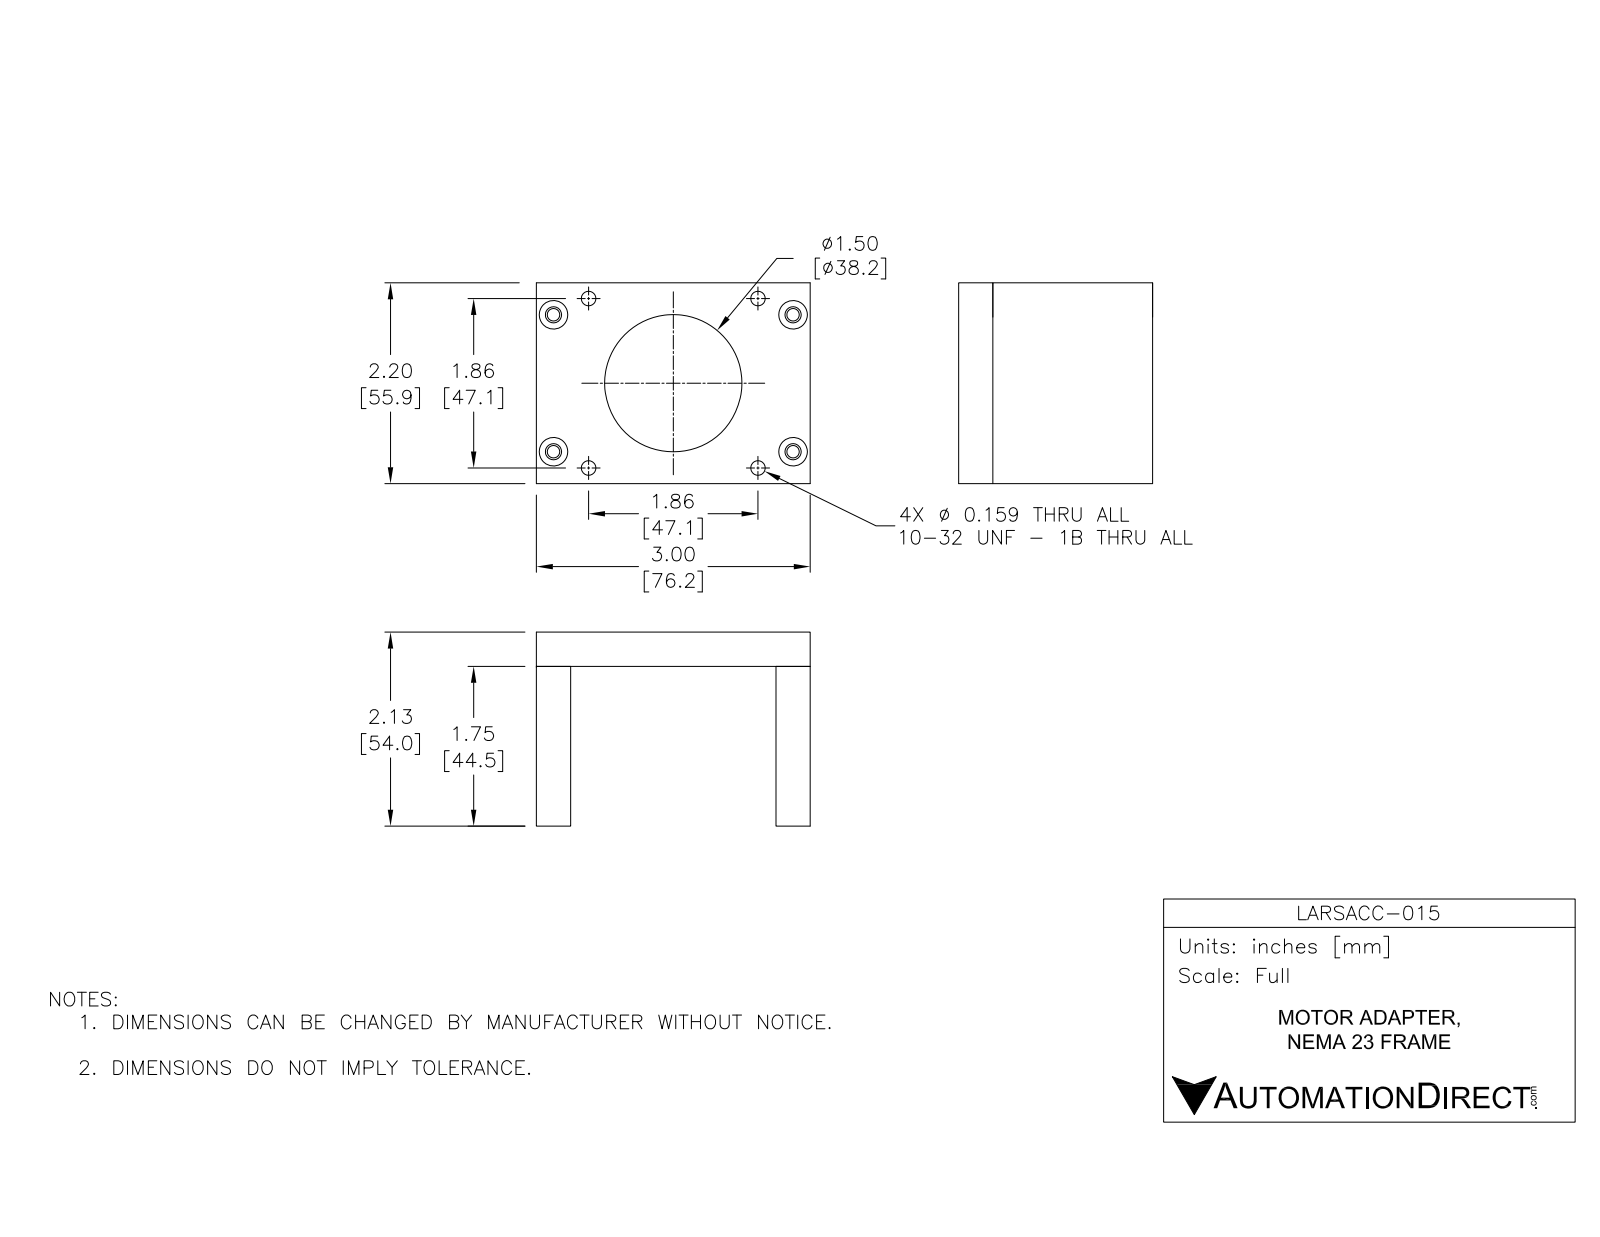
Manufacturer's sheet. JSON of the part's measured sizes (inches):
{"part_name": "LARSACC-015", "step_written_by": "SolidWorks 2015 (AUTOMOTIVE_DESIGN)", "units": "inches", "bodies": {"solids": 3, "faces": 88, "planar": 22, "cylindrical": 46, "other": 20}, "overall_size": [3, 2.2, 2.125], "volume_in3": 4.488, "surface_area_in2": 40.97, "round_holes": [[0.159, 10], [0.136, 4], [0.177, 4], [0.313, 4], [1.504, 1]], "face_to_face_distances": [0.375, 3, 2.625, 0.375, 2.25, 2.625, 2.2, 1.75, 2.125, 1.961], "hole_center_spacings": [2.625, 0.424, 0.25, 1.25, 1.312, 1.313, 1.479, 1.5]}
